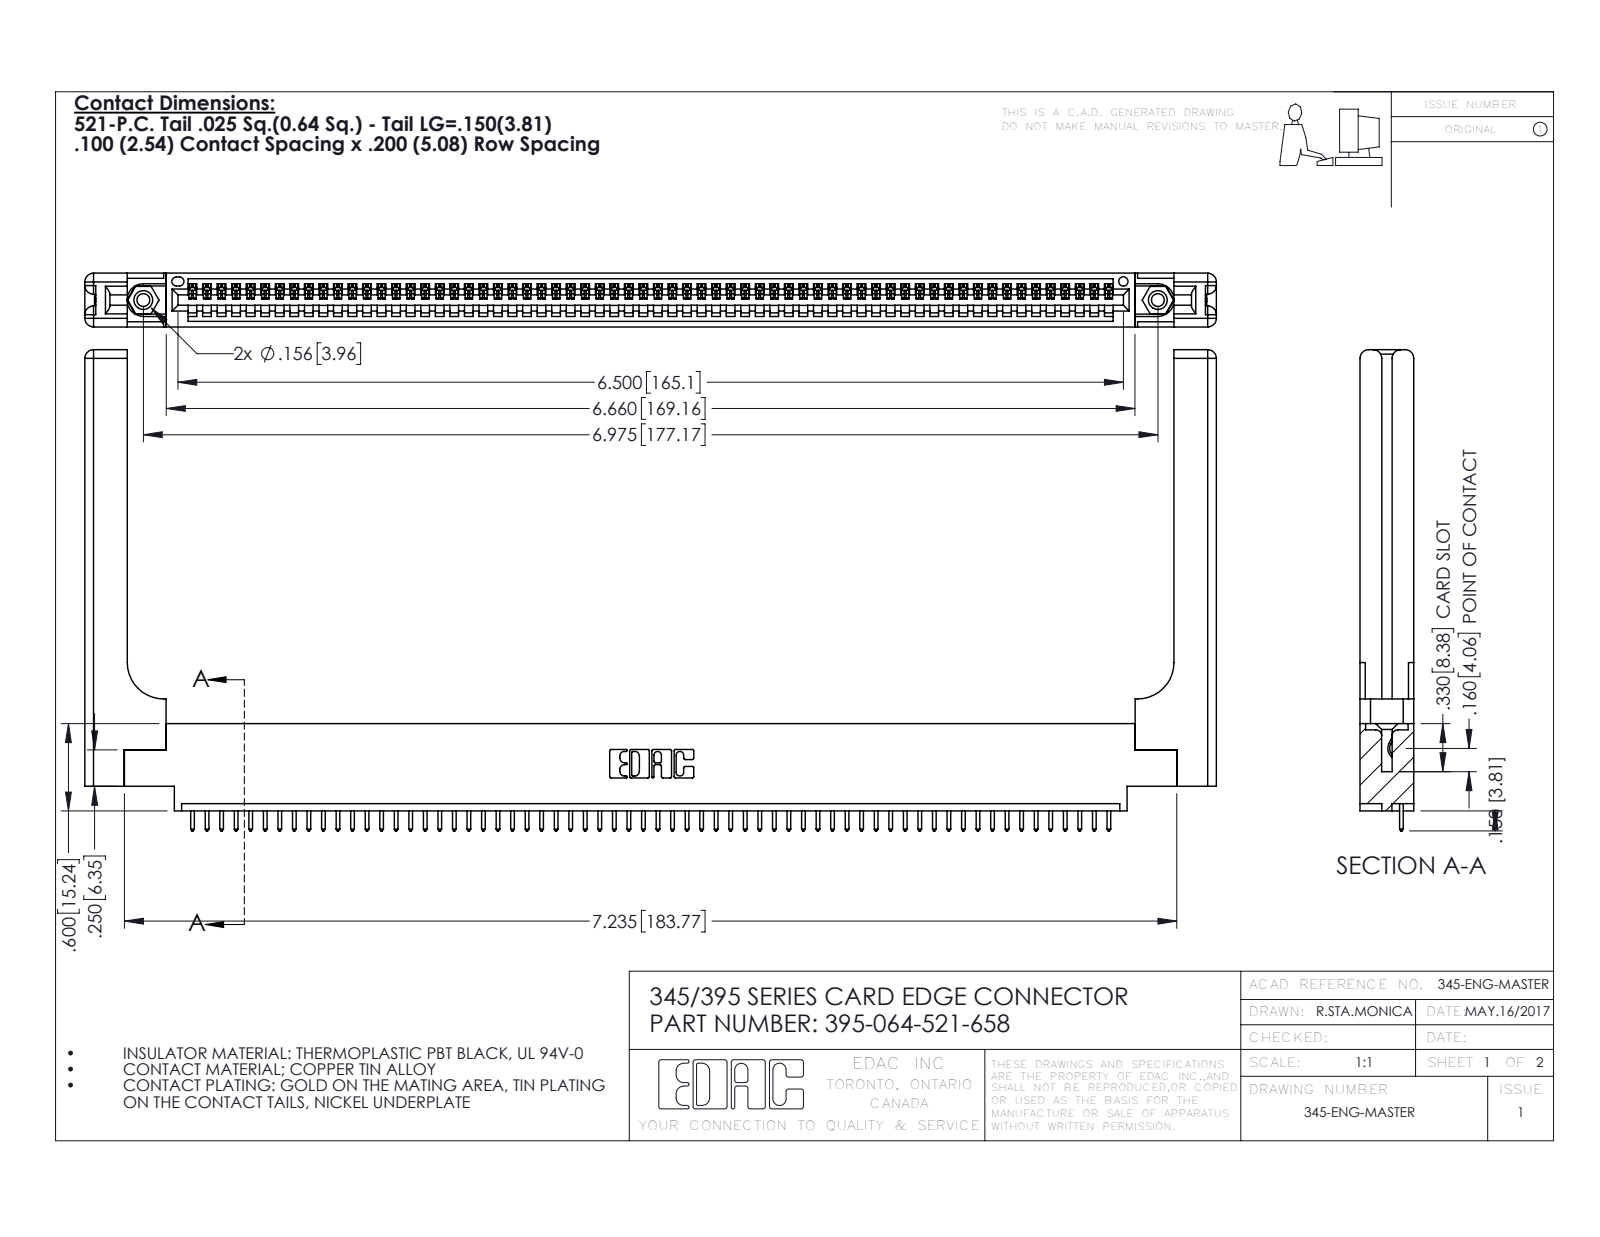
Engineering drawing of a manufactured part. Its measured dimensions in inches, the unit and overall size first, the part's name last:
Units: inches
Overall size (bounding box): 7.779 × 3.307 × 0.37
Round holes (diameter × count): ⌀0.089 ×2, ⌀0.125 ×2, ⌀0.156 ×2, ⌀0.064 ×1
Round bosses / shafts (diameter × count): ⌀0.155 ×2
Partial cylindrical surfaces — rounded edges, fillets, slot ends (radius × count): R0.006 ×128, R0.01 ×128, R0.01 ×22, R0.06 ×16, R0.007 ×6, R0.031 ×6, R0.026 ×3, R0.03 ×2
Main face-to-face distances: 0.072, 0.37, 0.298, 0.098, 0.272, 0.025, 0.2, 0.225, 0.148, 0.15
Hole centre spacings: 0.27, 6.739, 6.975
Volume: 1.657 in³ · Surface area: 46.2 in²
Bodies: 69 solids, 4098 faces (2792 planar, 1246 cylindrical, 60 other)
Part name (STEP PRODUCT): 345-250-001_345-250-001-102; 345 Part_0.170 Offset - 0.156 Dia-TH; 395-064-521-658; 345-220-058_345-220-058 (+1 more)
STEP written by: SolidWorks 2016 (CONFIG_CONTROL_DESIGN)
